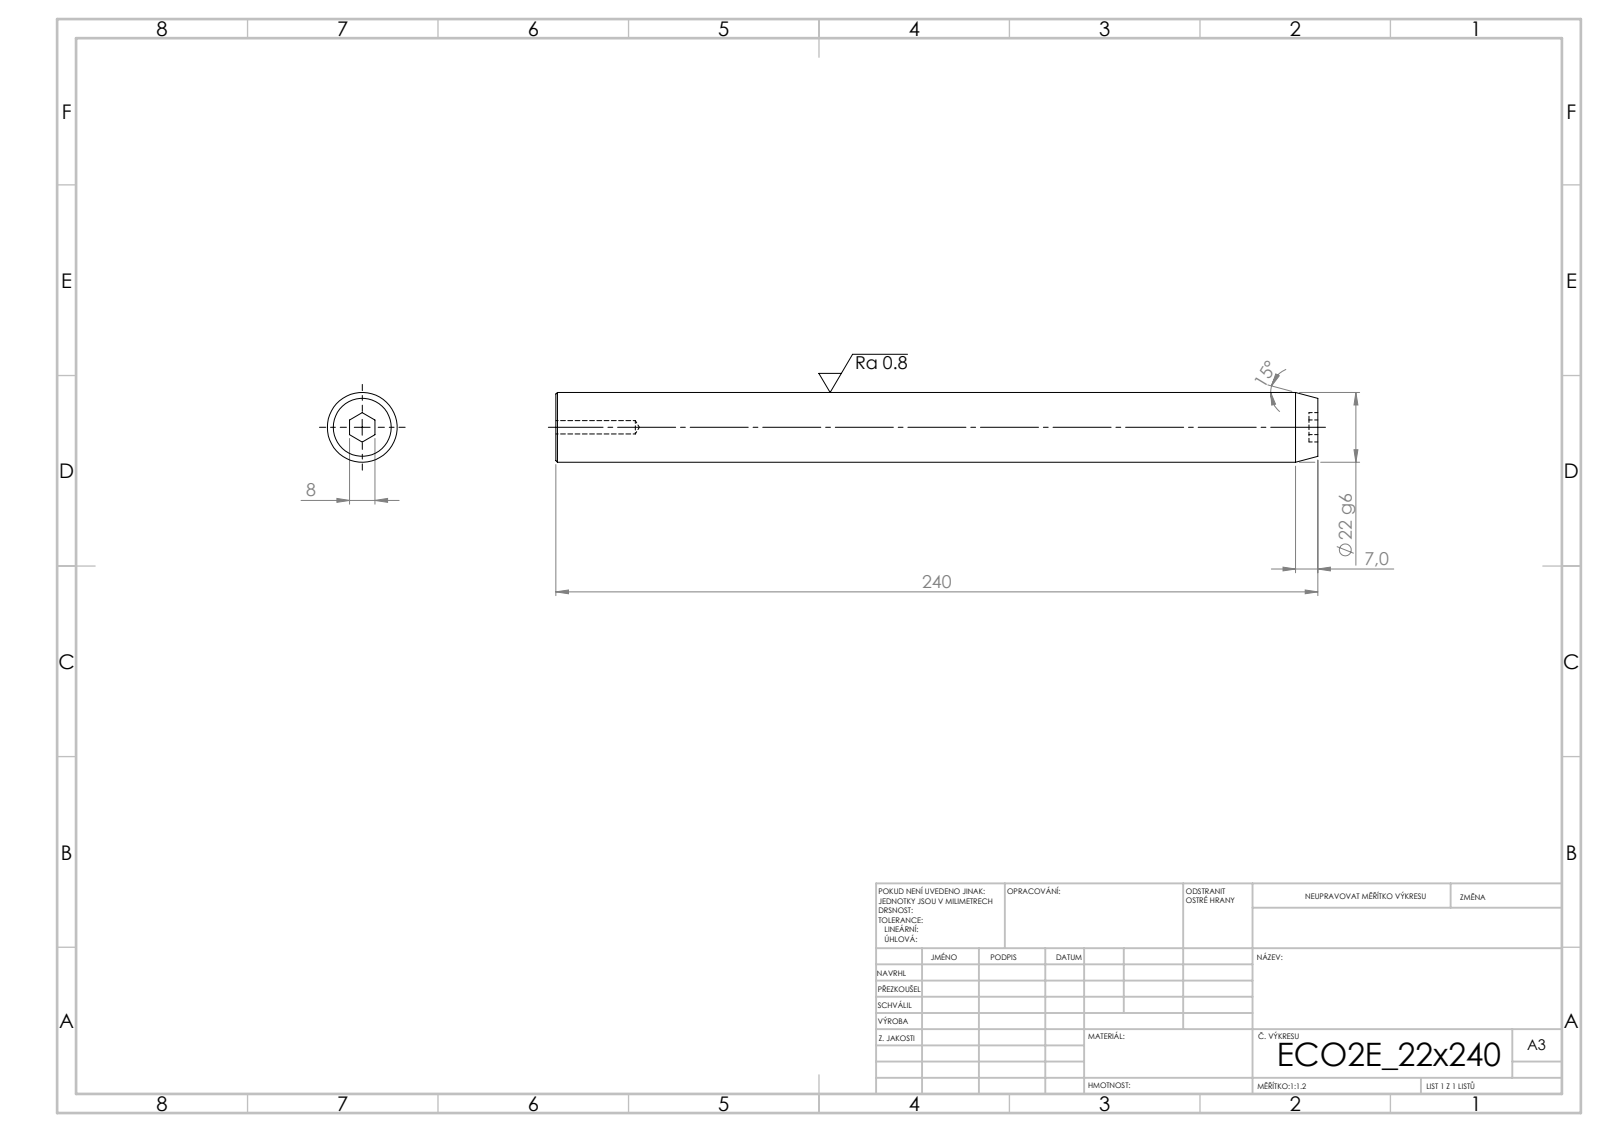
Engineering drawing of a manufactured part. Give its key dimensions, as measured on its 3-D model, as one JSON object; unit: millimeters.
{"step_written_by": "SolidWorks 2019 (CONFIG_CONTROL_DESIGN)", "units": "millimeters", "bodies": {"solids": 1, "faces": 19, "planar": 9, "cylindrical": 4, "other": 6}, "overall_size": [240, 22, 22], "volume_mm3": 90288, "surface_area_mm2": 17593, "round_holes": [[4.2, 1]], "round_bosses_or_shafts": [[22, 1]], "face_to_face_distances": [240, 2.8, 237.2, 8]}
